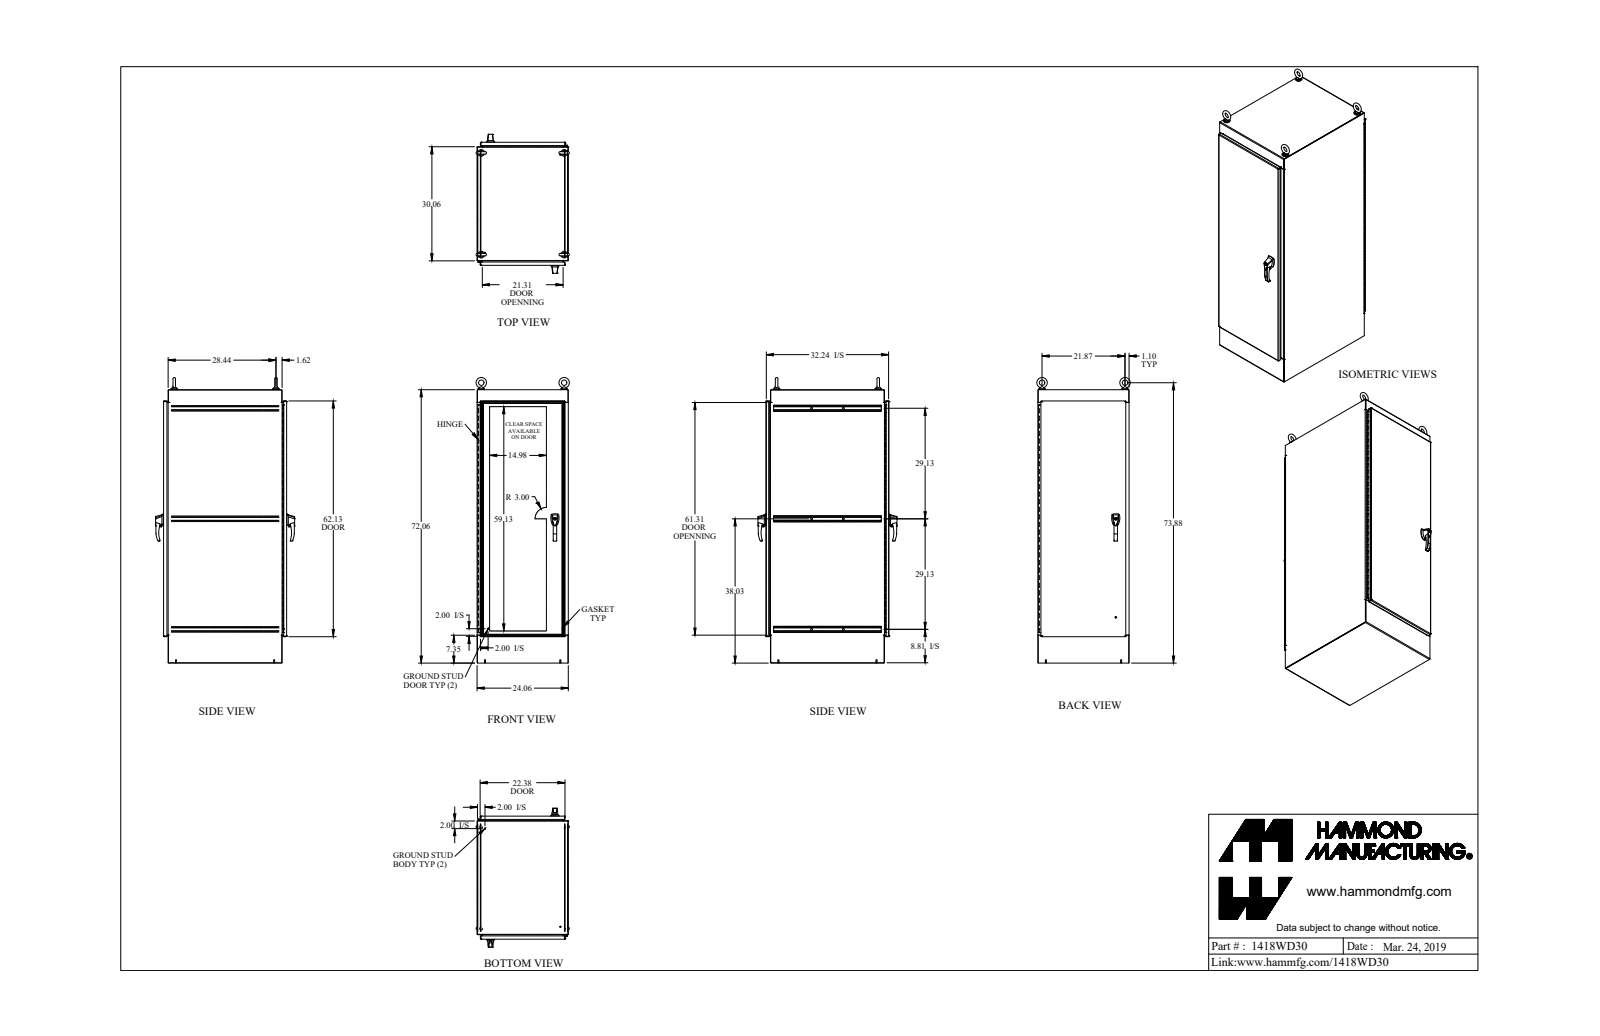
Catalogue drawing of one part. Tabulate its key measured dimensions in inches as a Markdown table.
| quantity | value |
| --- | --- |
| part name | 1418WD30_Default |
| STEP written by | SolidWorks 2019 (CONFIG_CONTROL_DESIGN) |
| units | inches |
| bodies | 91 solids, 3188 faces (1386 planar, 1476 cylindrical, 326 other) |
| overall size | 75.713 × 36.664 × 25.118 |
| volume | 1 150 in³ |
| surface area | 24 120 in² |
| round holes (diameter × count) | 0.304 × 20, 0.5 × 6, 0.25 × 4, 0.257 × 4, 0.28 × 4, 0.281 × 4, 0.313 × 4, 0.39 × 4, 0.413 × 4, 0.527 × 4, 0.625 × 4, 0.687 × 4 |
| round bosses / shafts (diameter × count) | 0.281 × 8, 1.75 × 4, 1.5 × 4, 1.25 × 4, 1 × 4, 0.75 × 4, 0.738 × 4, 0.63 × 4 |
| partial cylindrical surfaces (radius × count) | 0.125 × 44, 0.043 × 42, 0.138 × 36, 0.017 × 32, 0.048 × 24, 0.143 × 24, 0.06 × 16, 0.318 × 14 |
| main face-to-face distances | 0.095, 23.965, 32.339, 23.87, 24.06, 31.152, 1.187, 32.244, 71.965, 32.434 |
| hole center spacings | 6, 23.125, 12, 25.352, 18, 28.683, 24, 32.783 |
